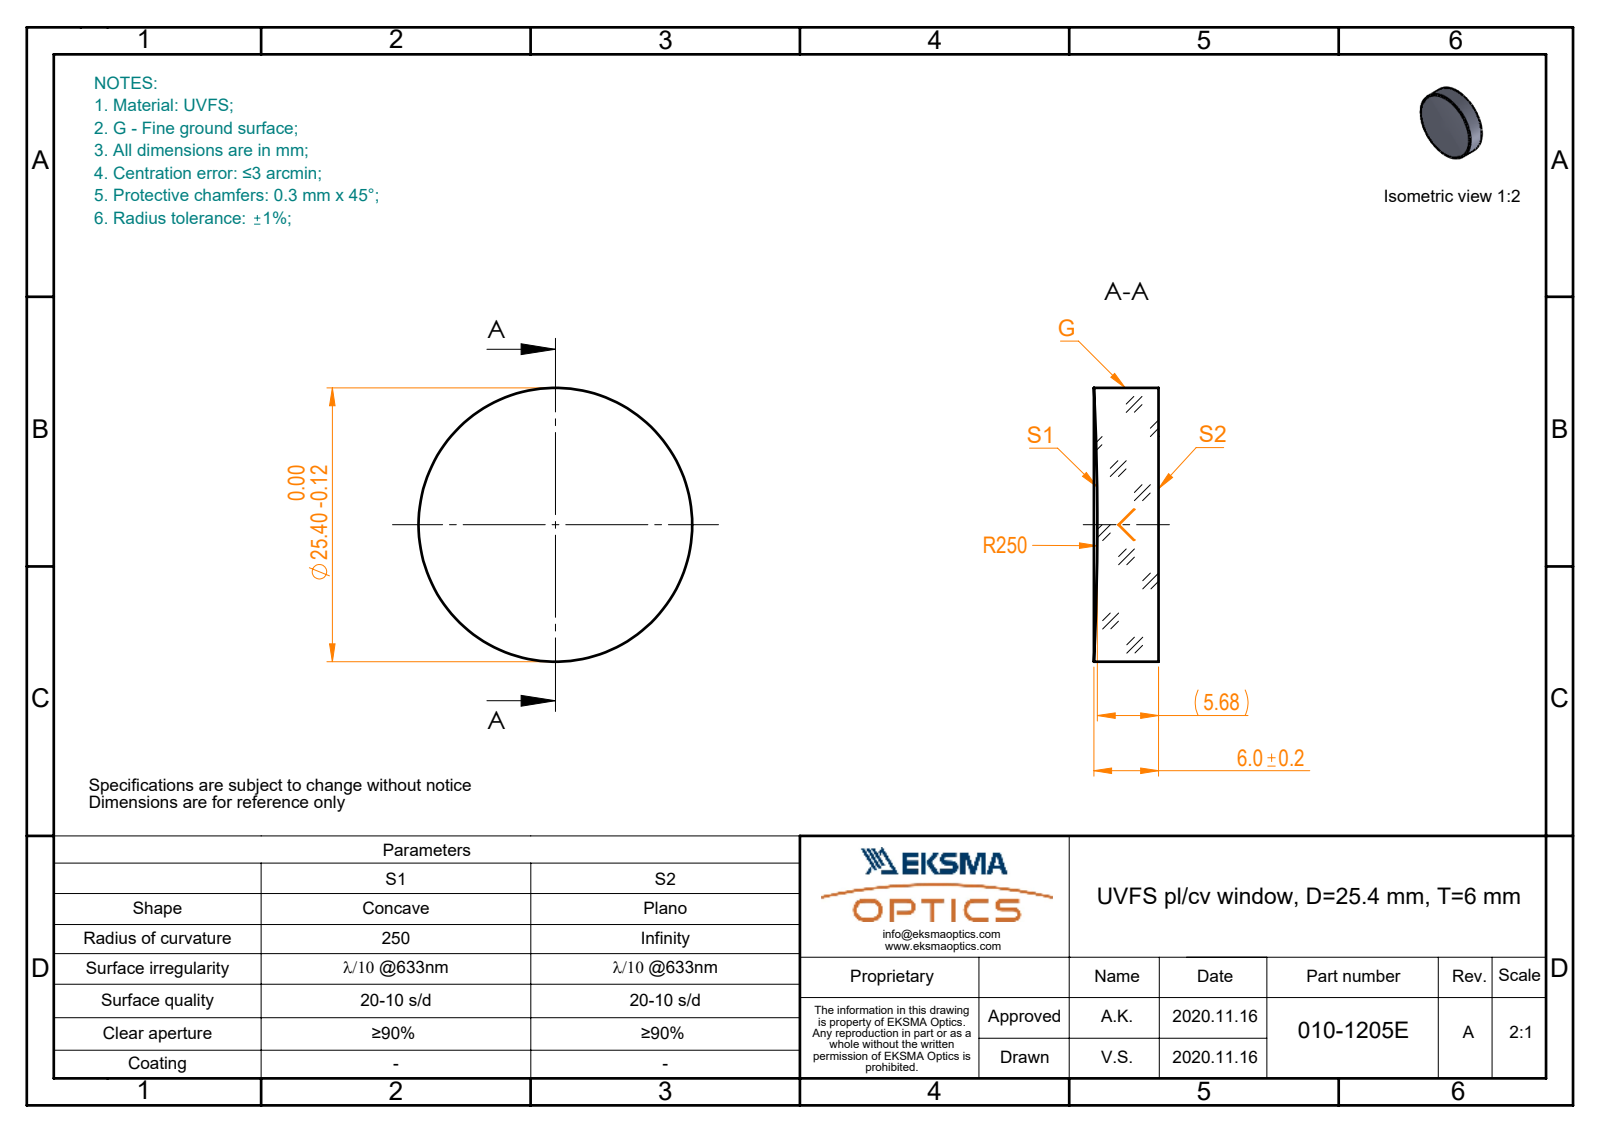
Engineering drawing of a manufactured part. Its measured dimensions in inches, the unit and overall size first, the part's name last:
Units: inches
Overall size (bounding box): 1 × 1 × 0.236
Round bosses / shafts (diameter × count): ⌀1 ×1
Volume: 0.181 in³ · Surface area: 2.314 in²
Bodies: 1 solid, 5 faces (1 planar, 2 cylindrical, 2 other)
Part name (STEP PRODUCT): 010-1205E_UVFS_PCV_window
STEP written by: SolidWorks 2019 (CONFIG_CONTROL_DESIGN)
